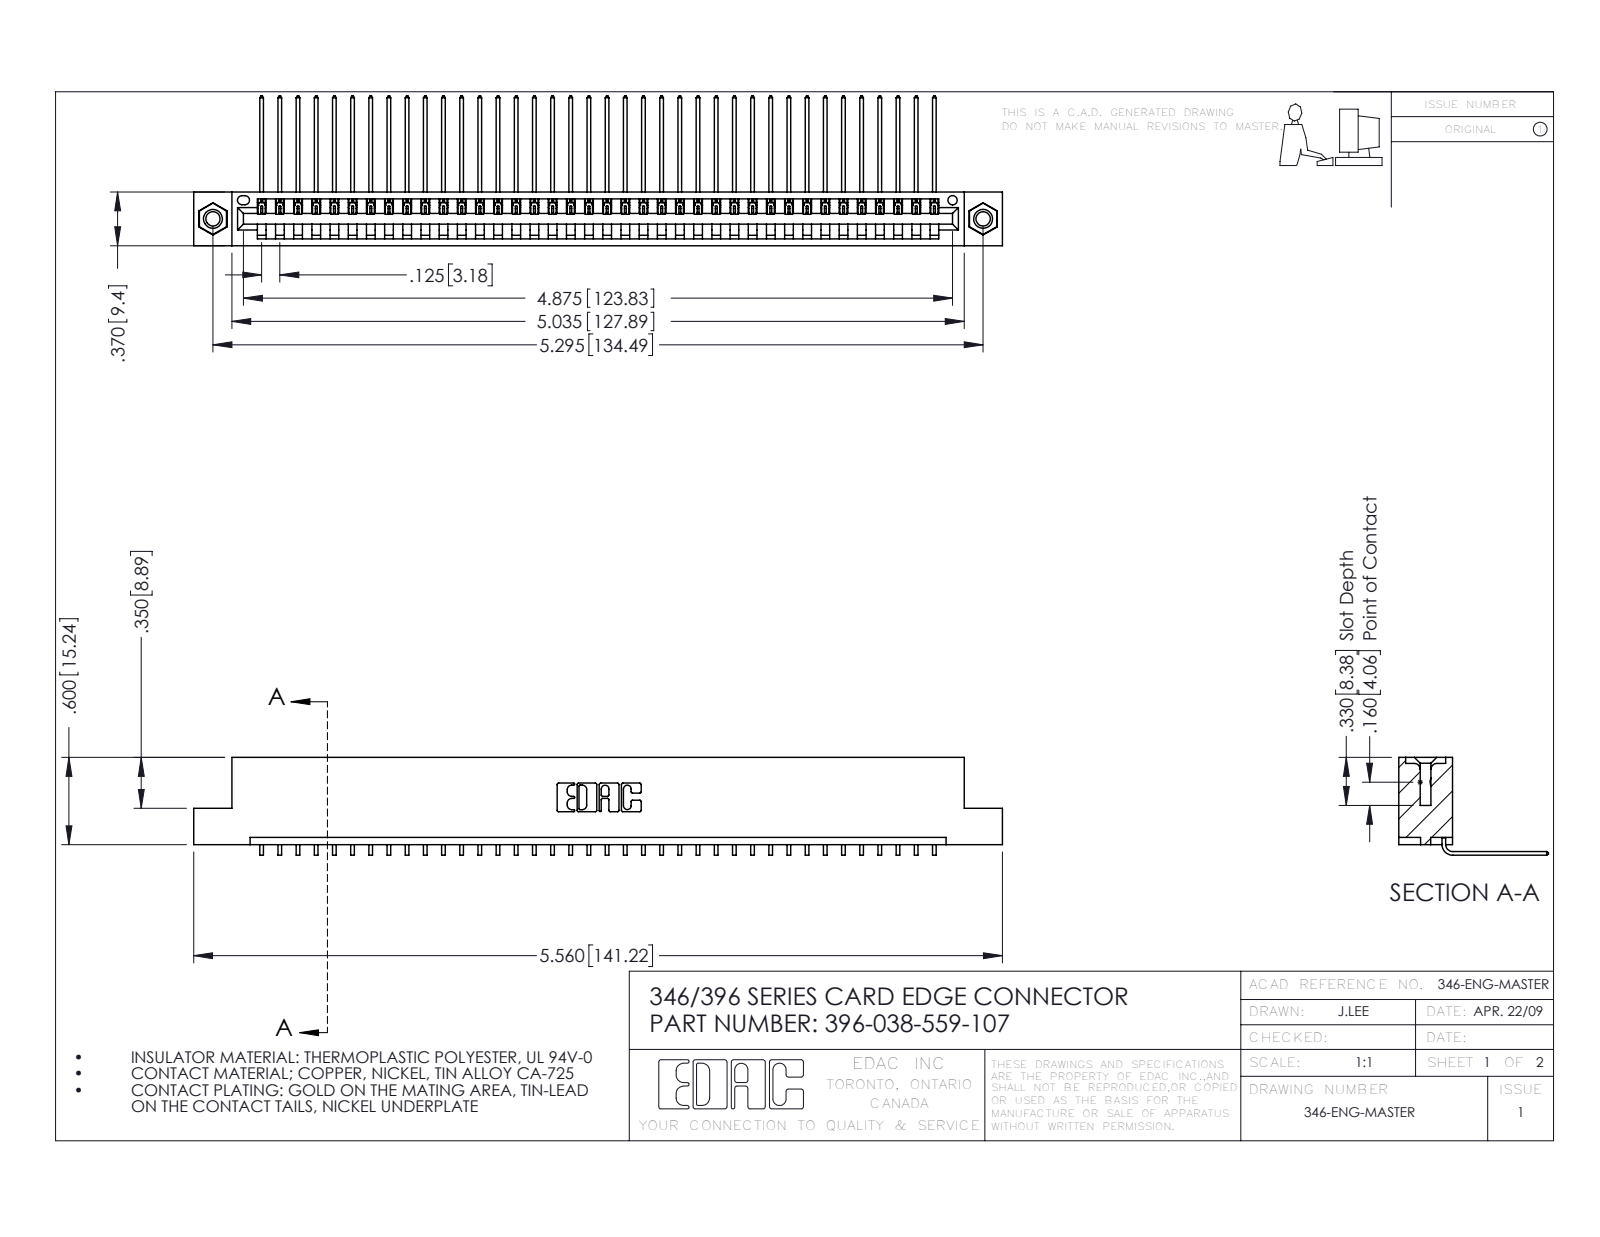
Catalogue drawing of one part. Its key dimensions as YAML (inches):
part_name: "396-038-559-107; 345-292-001_558 559 Tail - 1; 345-250-001_345-250-005-103; 346 Part_Flush Mounting Lugs - 0.156 Dia-TI"
step_written_by: "SolidWorks 2016 (CONFIG_CONTROL_DESIGN)"
units: inches
bodies: {solids: 41, faces: 2462, planar: 1704, cylindrical: 742, other: 16}
overall_size: [5.56, 1.03, 0.673]
volume: 0.83
surface_area: 27.51
round_holes:
  - {diameter: 0.098, count: 2}
  - {diameter: 0.125, count: 2}
  - {diameter: 0.156, count: 2}
  - {diameter: 0.064, count: 1}
round_bosses_or_shafts:
  - {diameter: 0.155, count: 2}
partial_cylinders:
  - {radius: 0.006, count: 76}
  - {radius: 0.01, count: 22}
  - {radius: 0.007, count: 6}
  - {radius: 0.031, count: 6}
  - {radius: 0.026, count: 3}
  - {radius: 0.031, count: 2}
  - {radius: 0.04, count: 2}
  - {radius: 0.014, count: 1}
face_to_face_distances: [0.048, 0.322, 0.37, 0.025, 0.25, 0.072, 0.298, 0.148, 0.222, 0.1]
hole_center_spacings: [0.246, 5.086, 5.295]
